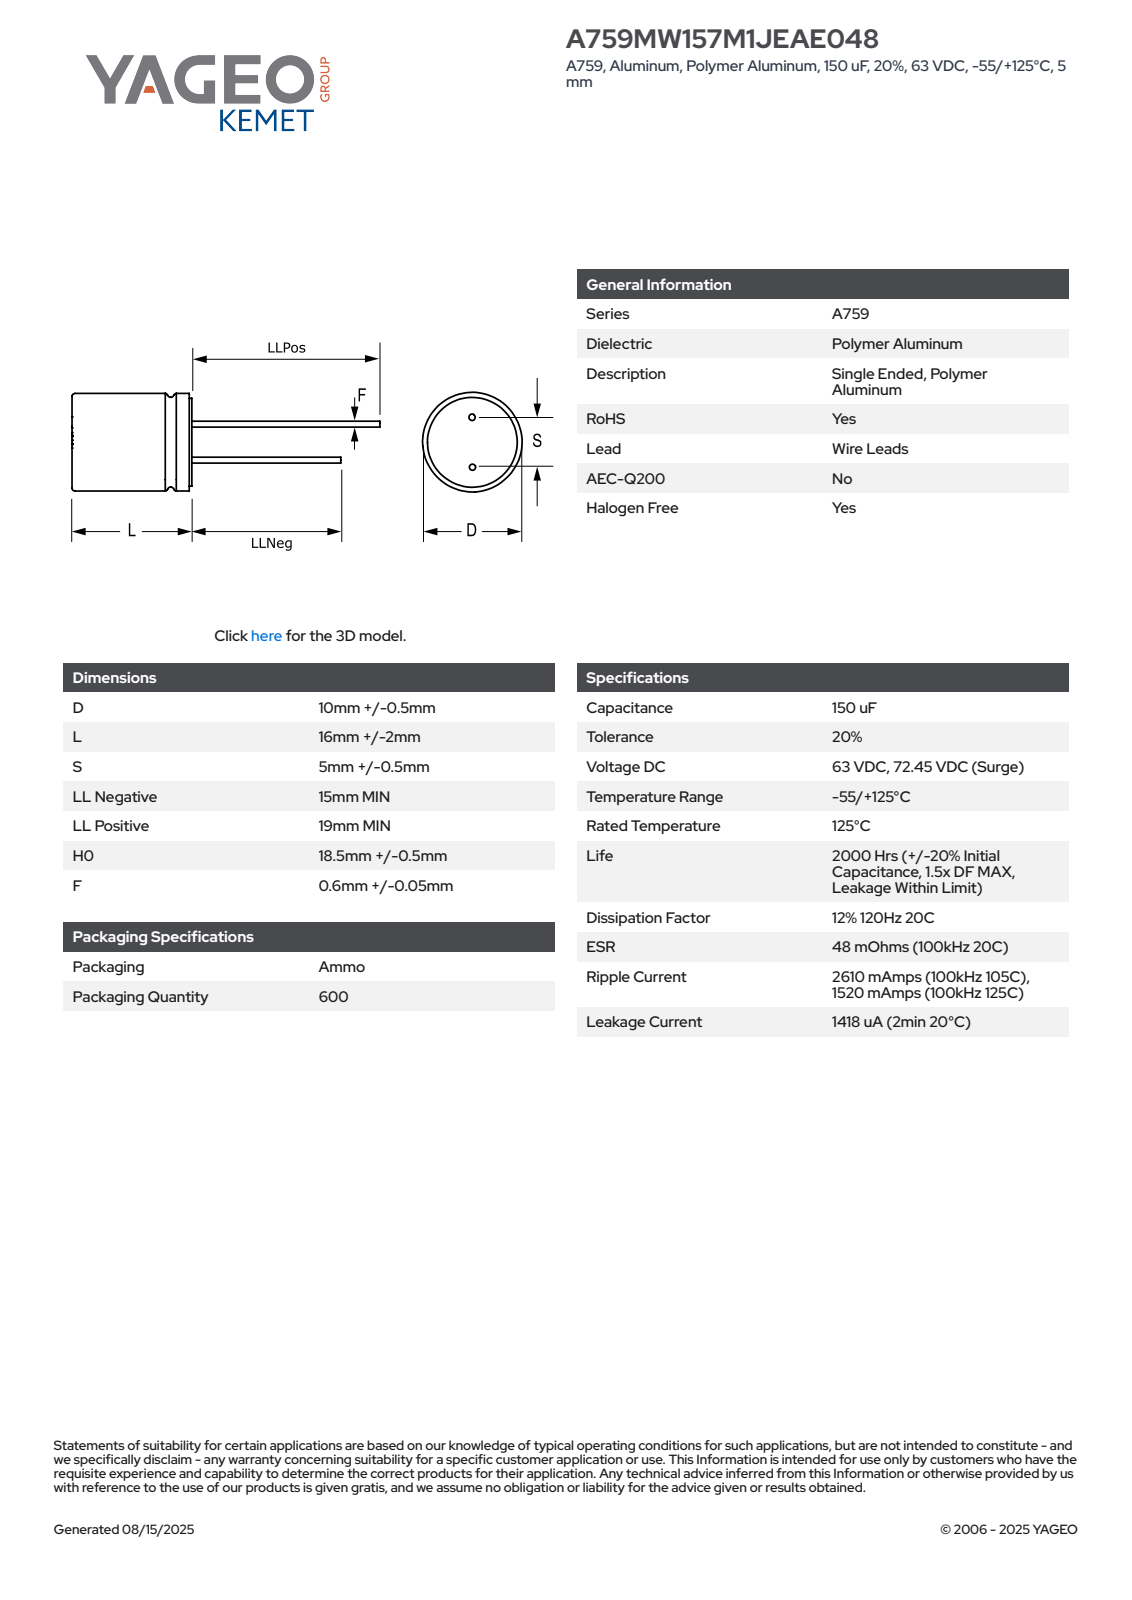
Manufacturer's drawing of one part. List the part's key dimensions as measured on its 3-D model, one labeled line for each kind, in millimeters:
Part name (STEP PRODUCT): CAR_KP_10X16_D10.5L18S5F0.65
STEP written by: SolidWorks 2014 (AUTOMOTIVE_DESIGN)
Units: millimetres
Bodies: 4 solids, 75 faces (61 planar, 8 cylindrical, 6 other)
Overall size (bounding box): 37.01 × 10.5 × 10.5
Volume: 1 554 mm³ · Surface area: 859 mm²
Round bosses / shafts (diameter × count): ⌀0.65 ×2, ⌀10.5 ×1
Main face-to-face distances: 18, 18.01, 33.01, 37.01, 33, 37, 15, 19, 4, 1.15
